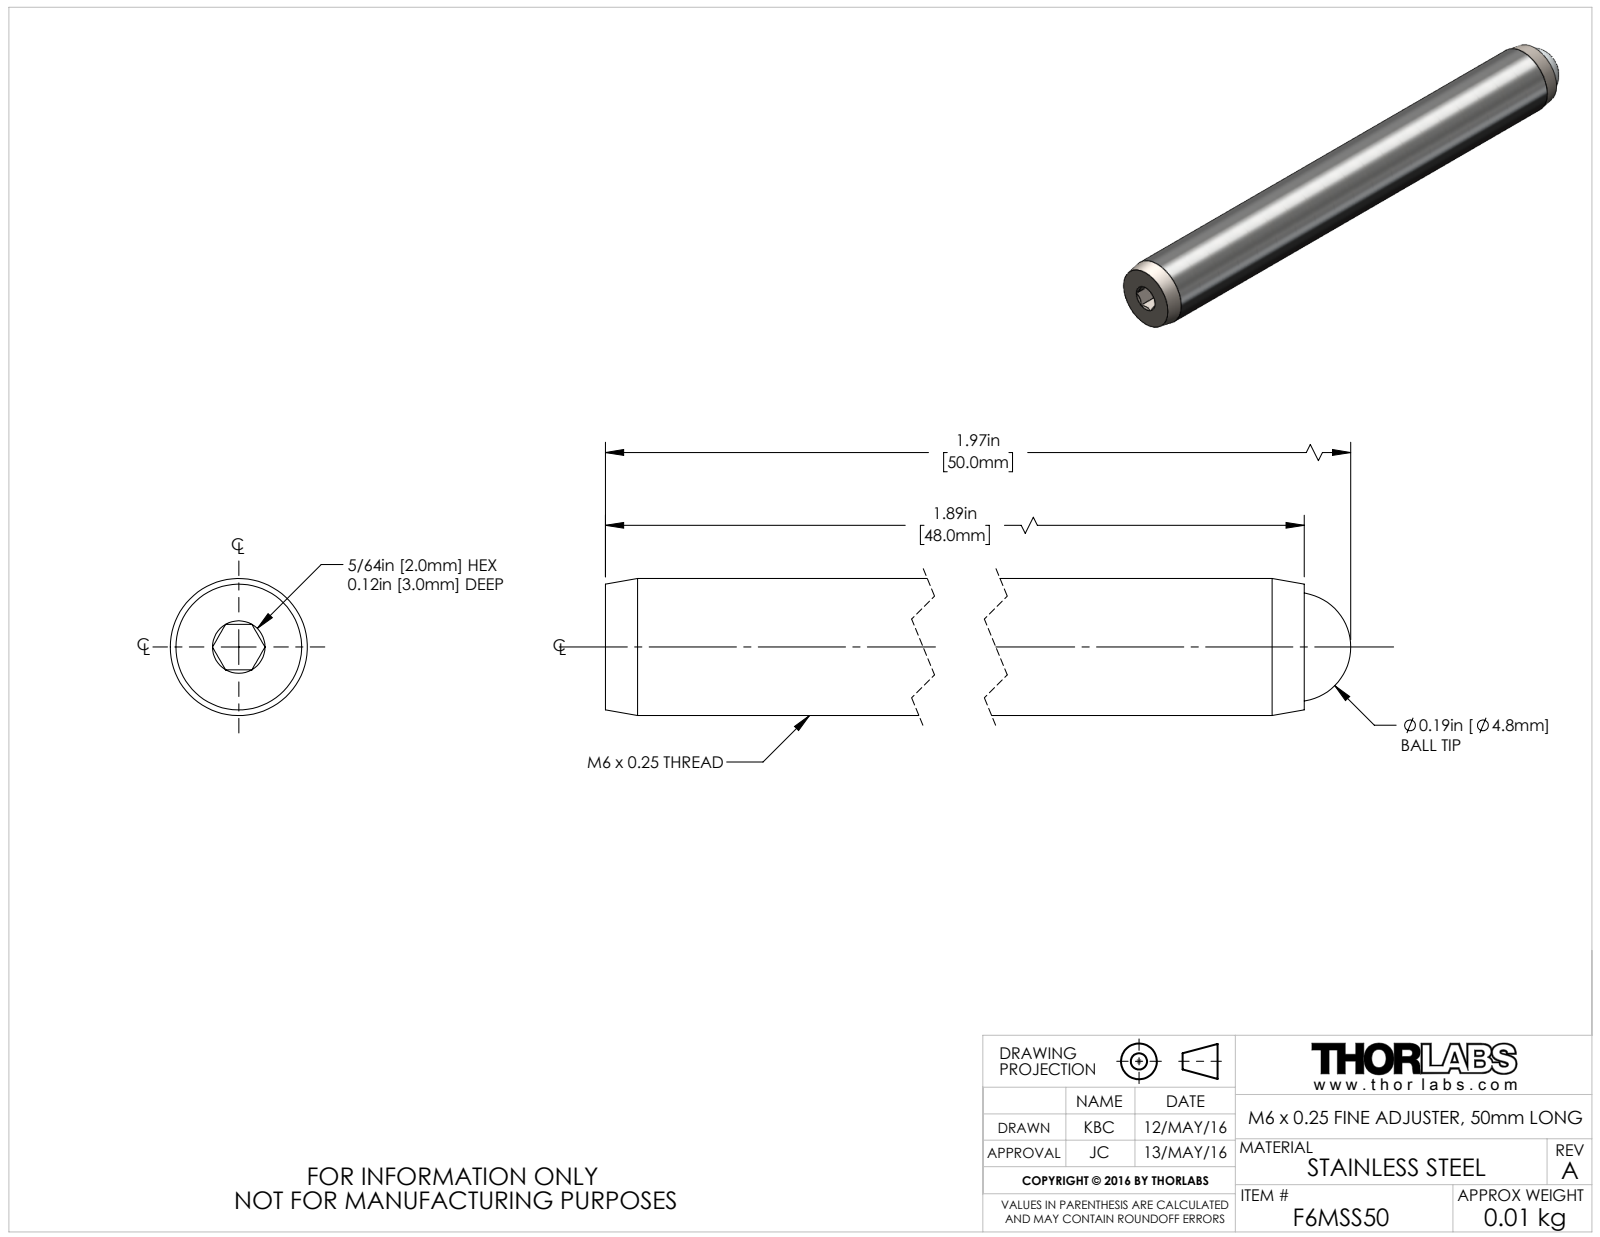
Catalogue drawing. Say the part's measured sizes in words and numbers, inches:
The part is named "TTN102534-E0W". Its 3-D file was written by "SolidWorks 2016 (CONFIG_CONTROL_DESIGN)". It is 2 solids with 27 faces: 9 planar, 4 cylindrical and 14 other. Overall it measures 1.97 by 0.235 by 0.235 inches. Its volume is 0.082 cubic inches and its surface area 1.654 square inches. Round holes: 1 of diameter 0.188. Round bosses or shafts: 1 of diameter 0.235. The main face-to-face distances are 0.078, 1.89, 0.12, 1.77.
